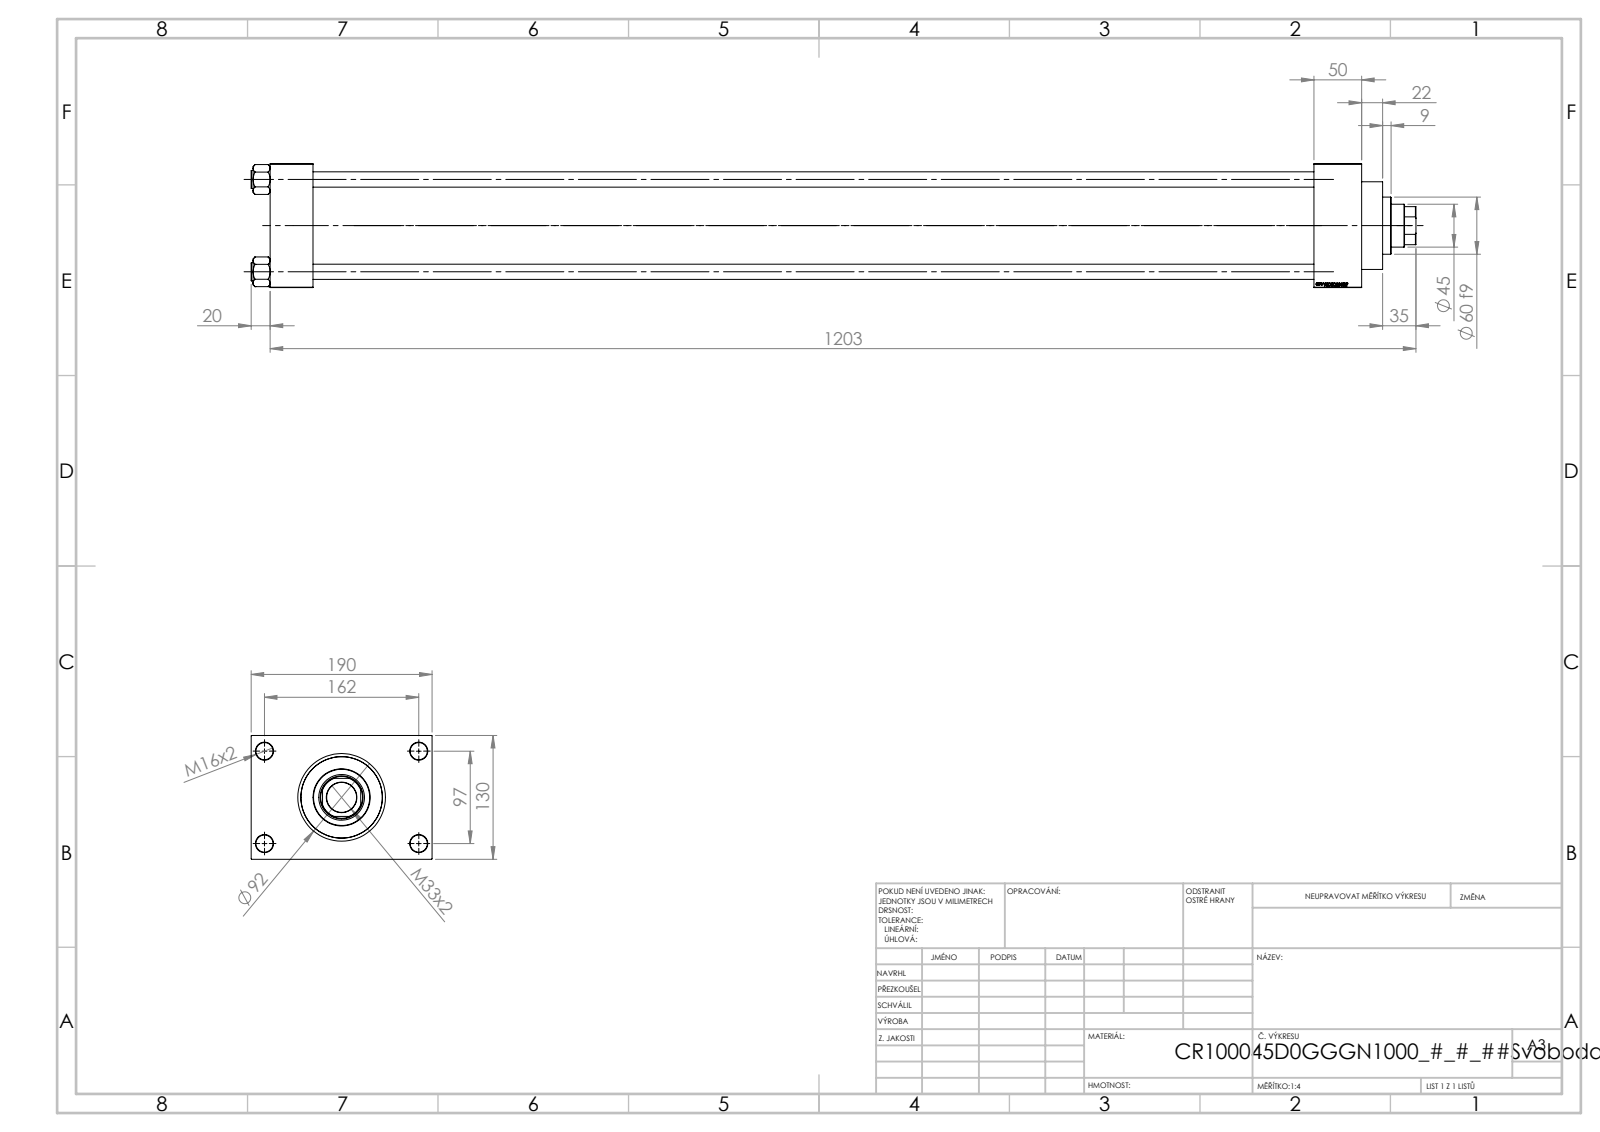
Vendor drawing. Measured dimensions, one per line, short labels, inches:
name: V215CR_VCP_D; V215_VC_A; V215CR_D_Body; V215CR_D_TYCINKA (+1 more)
written by: SolidWorks 2019 (CONFIG_CONTROL_DESIGN)
unit: in
bodies: 11 solids, 1152 faces (545 planar, 89 cylindrical, 518 other)
size: 48.15 × 7.48 × 5.118
volume: 360.3 in³; area: 2 049 in²
holes: 4× ⌀0.63, 4× ⌀0.709, 2× ⌀0.276, 2× ⌀1.041, 2× ⌀1.378, 1× ⌀1.24, 1× ⌀1.772, 1× ⌀1.89, 1× ⌀2.992, 1× ⌀3.366, 1× ⌀3.937
bosses: 4× ⌀0.748, 1× ⌀4.173, 1× ⌀3.622, 1× ⌀2.362
rounds: 1× R0.866
face distances: 5.118, 1.772, 43.15, 41.378, 45.118, 43.346, 1.969, 1.181, 6.299, 7.48
hole spacings: 1.281, 2.698, 3.717, 3.815, 4.026, 5.096, 6.367, 3.819
